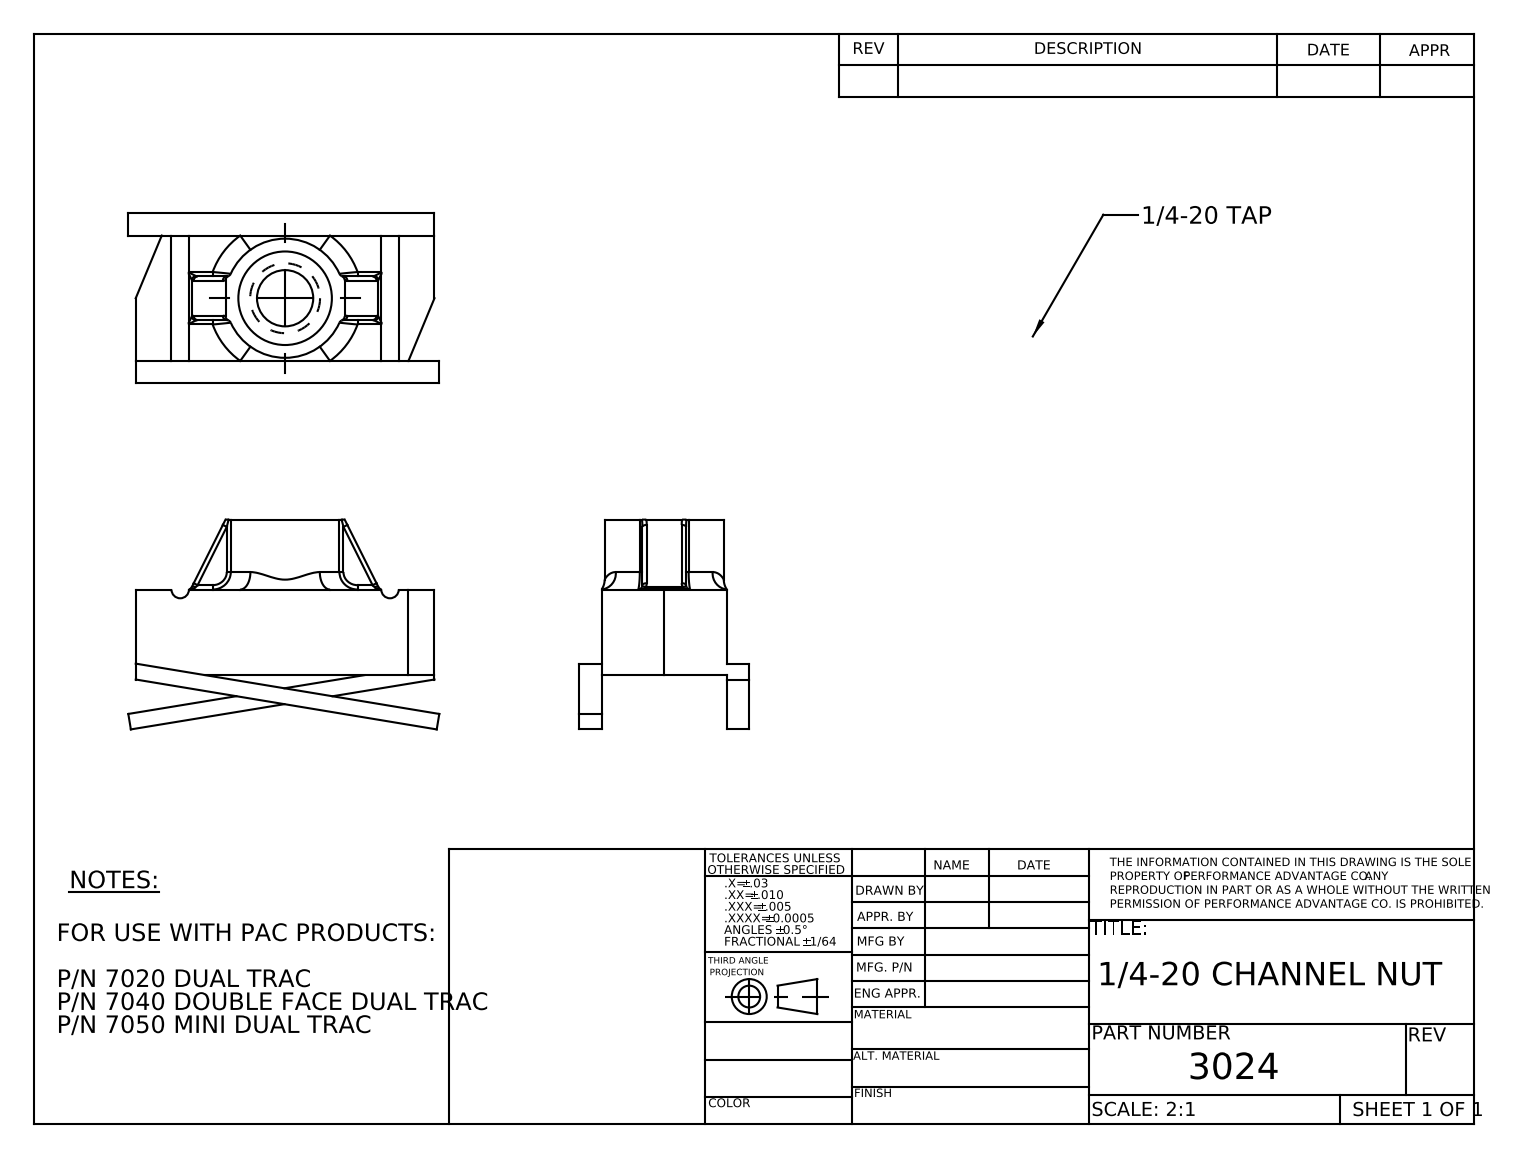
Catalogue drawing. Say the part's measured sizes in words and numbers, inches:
The part is named "3024". Its 3-D file was written by "SolidWorks 2010 (CONFIG_CONTROL_DESIGN)". It is 1 solid with 77 faces: 31 planar, 24 cylindrical and 22 other. Overall it measures 1.112 by 0.75 by 0.608 inches. Its volume is 0.172 cubic inches and its surface area 3.052 square inches. Round holes: 1 of diameter 0.201, 1 of diameter 0.334. Partial cylindrical surfaces (rounded edges, fillets, slot ends): 12 of radius 0.016, 2 of radius 0.031, 1 of radius 0.213. The main face-to-face distances are 0.448, 0.056, 0.306, 0.08, 0.528, 0.987, 1.068, 0.608, 0.556, 0.25.
